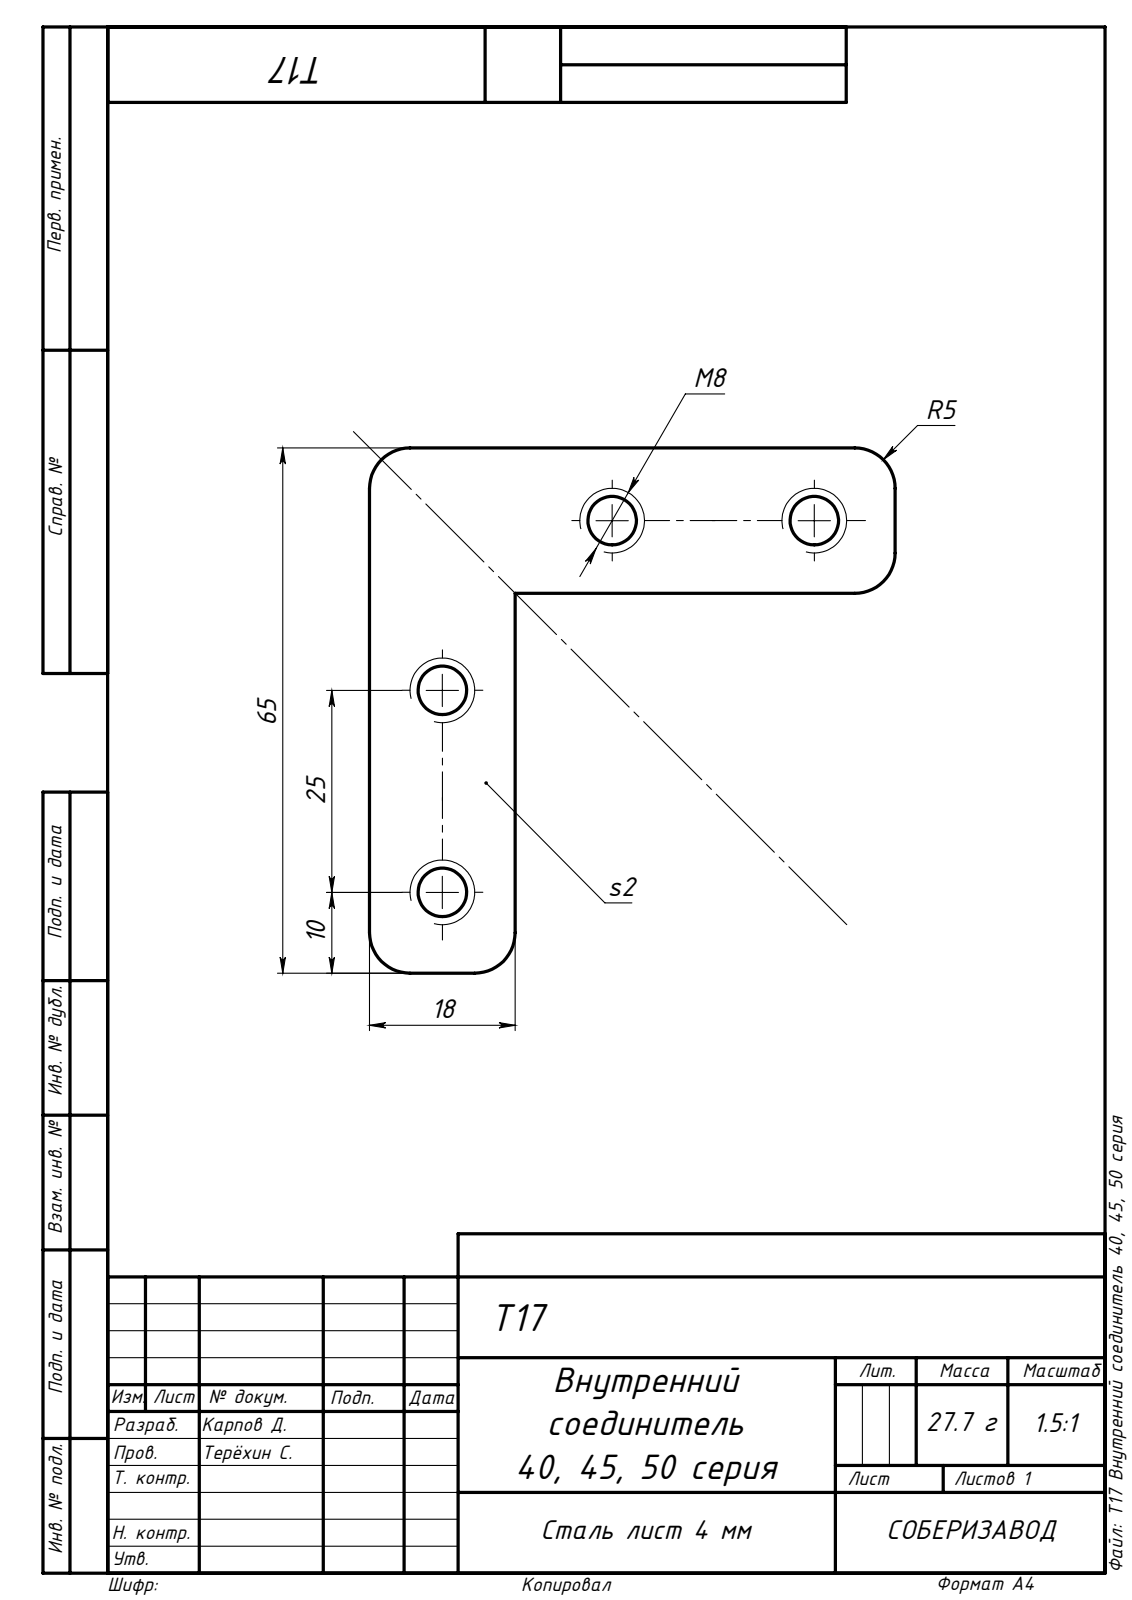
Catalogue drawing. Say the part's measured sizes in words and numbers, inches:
The part is named "T17 Внутренний соединитель 40, 45, 50 серия". Its 3-D file was written by "SolidWorks 2021 (AUTOMOTIVE_DESIGN)". It is 1 solid with 21 faces: 8 planar, 13 cylindrical and 0 other. Overall it measures 2.559 by 2.559 by 0.157 inches. Its volume is 0.458 cubic inches and its surface area 7.829 square inches. Round holes: 4 of diameter 0.236. Partial cylindrical surfaces (rounded edges, fillets, slot ends): 5 of radius 0.197. The main face-to-face distances are 0.157, 0.709, 2.559, 1.85. The hole center spacings are 0.984, 1.991, 1.169, 2.561.
